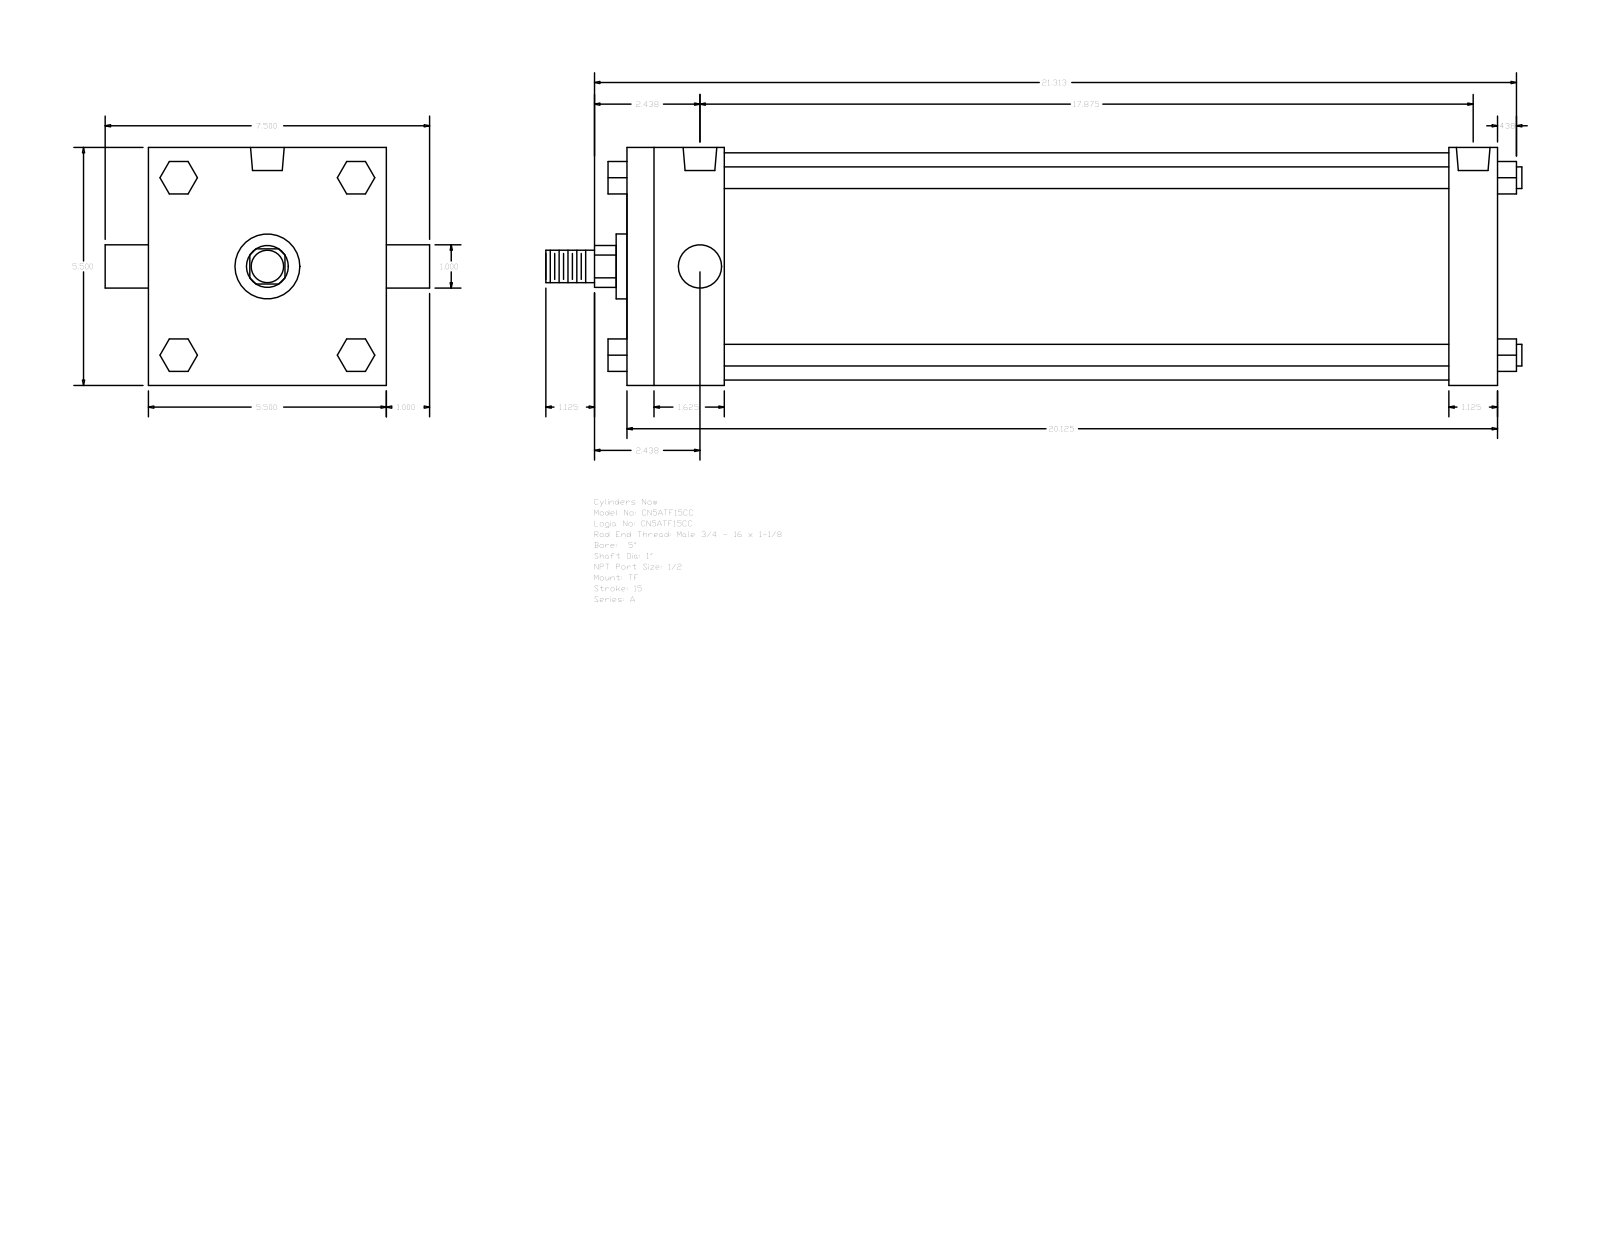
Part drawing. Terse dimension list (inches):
name: A_TF__0500_1
written by: GSSL Pune (CONFIG_CONTROL_DESIGN)
unit: in
bodies: 0 solids, 120 faces (92 planar, 28 cylindrical, 0 other)
size: 22.563 × 7.5 × 5.5
holes: 3× ⌀0.344, 2× ⌀0.778
bosses: 4× ⌀0.5, 2× ⌀1, 1× ⌀5.25, 1× ⌀1.5, 1× ⌀0.75
rounds: 1× R0.484
face distances: 5.5, 20.125, 19, 1.125, 2.25, 16.75, 17.875, 0.75, 2.05, 3.55
hole spacings: 0.094, 17.781, 17.687, 17.875
